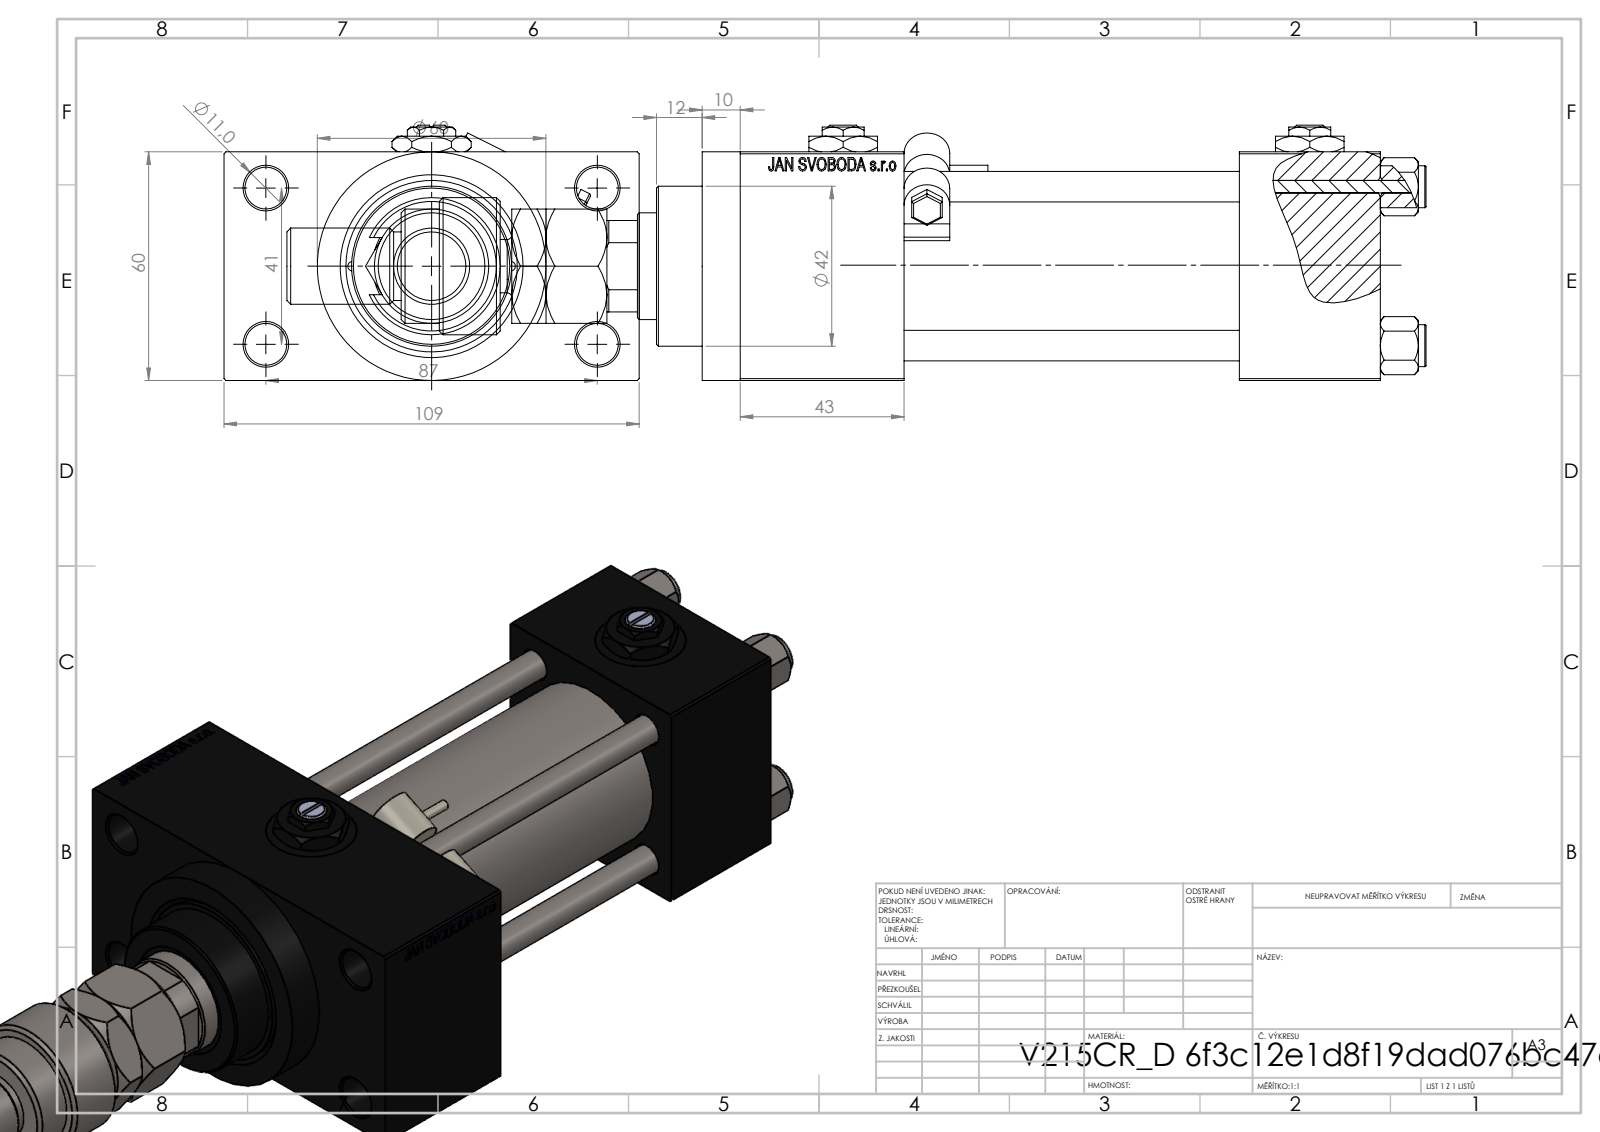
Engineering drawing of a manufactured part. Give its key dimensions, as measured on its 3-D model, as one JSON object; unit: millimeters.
{"part_name": "FEMALE_PART_FOR_DFA; MFA; NUT_M5_D; MSRF_MSRG1 (+5 more)", "step_written_by": "SolidWorks 2019 (CONFIG_CONTROL_DESIGN)", "units": "millimeters", "bodies": {"solids": 16, "faces": 1332, "planar": 596, "cylindrical": 130, "other": 606}, "overall_size": [299, 109, 67], "volume_mm3": 615598, "surface_area_mm2": 160870, "round_holes": [[8, 4], [11, 4], [16.66, 4], [24, 4], [7, 3], [2.5, 2], [18.5, 1], [28, 1], [31, 1], [40, 1], [45, 1]], "round_bosses_or_shafts": [[11, 4], [60, 1], [46, 1], [42, 1], [36, 1], [30, 1], [22, 1], [20, 1]], "partial_cylinders_radius": [[0.5, 6], [6, 2], [7.5, 1], [12, 1], [13.5, 1]], "face_to_face_distances": [60, 88, 24.5, 84.5, 37, 125, 43, 168, 131, 109], "hole_center_spacings": [20.85, 22.65, 29.49, 30.62, 41.7, 46.53, 47.15, 48.09]}
